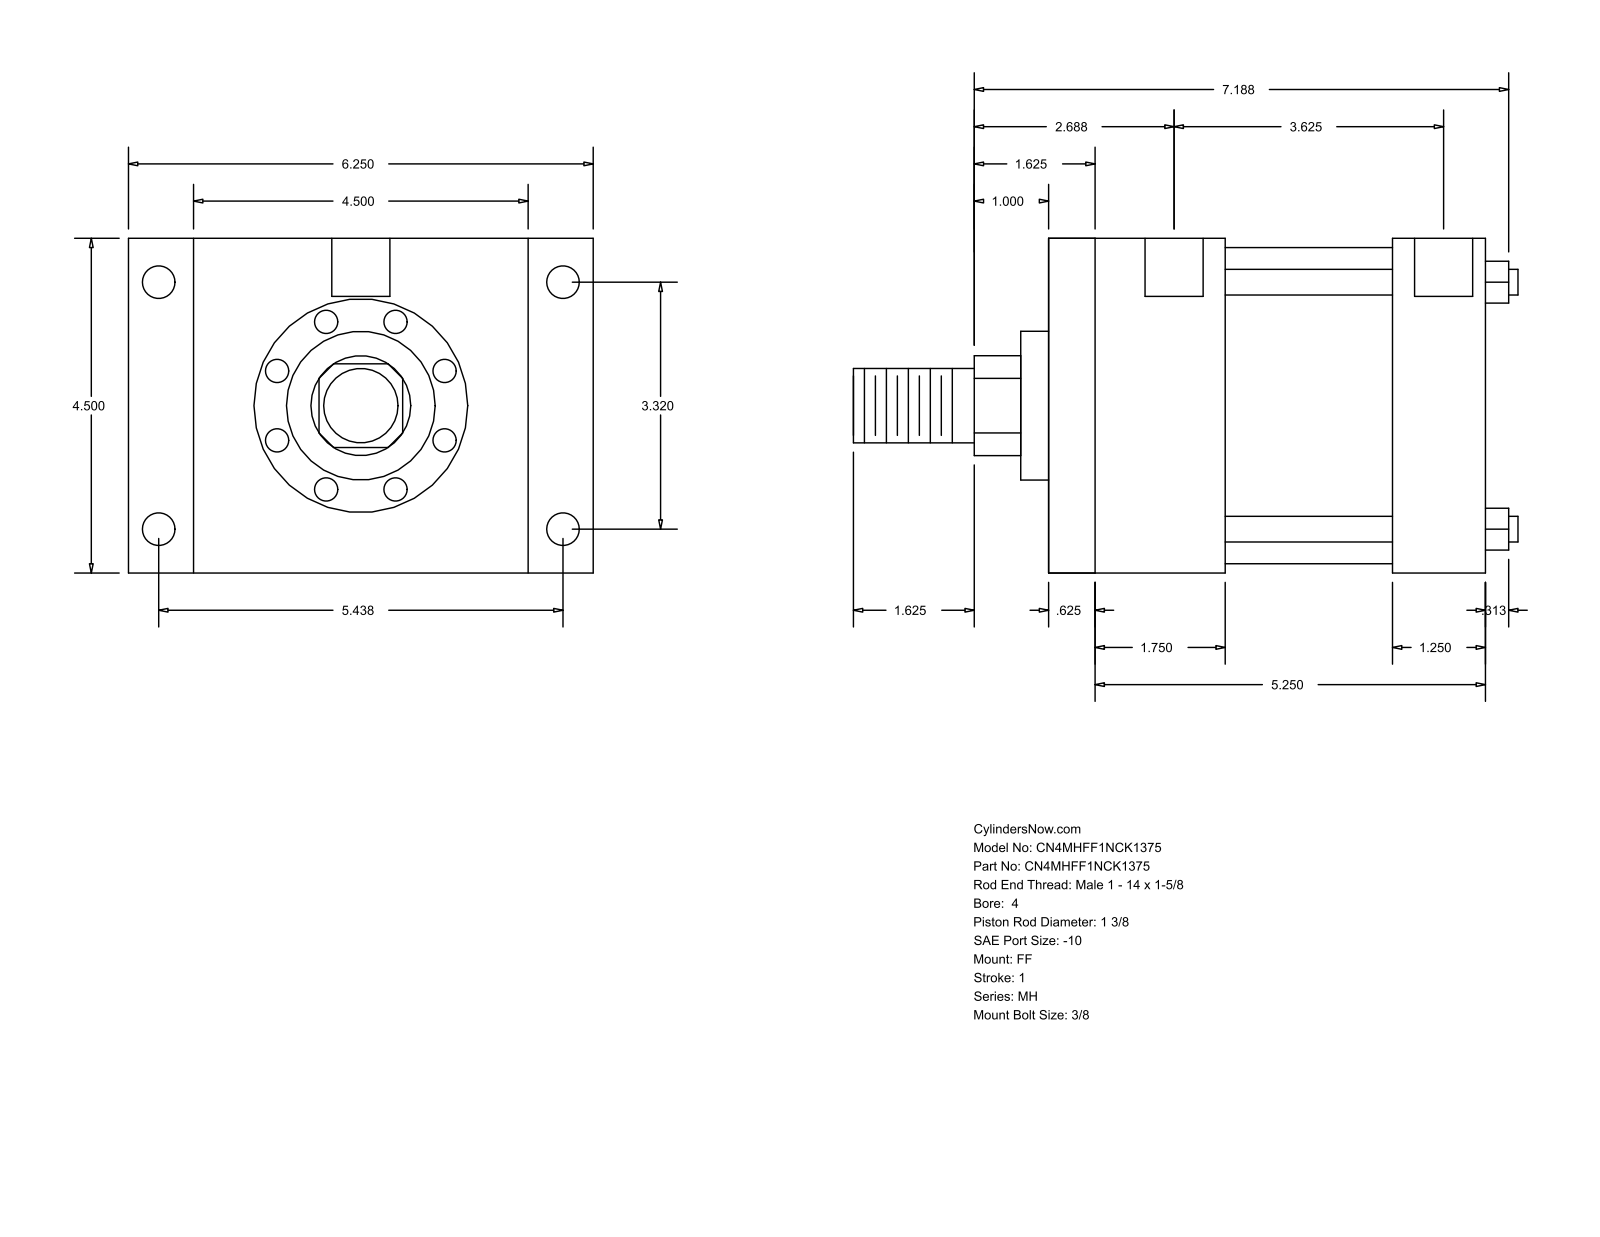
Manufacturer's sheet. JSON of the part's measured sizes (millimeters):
{"part_name": "MH_FF__0400_1.375", "step_written_by": "GSSL Pune (CONFIG_CONTROL_DESIGN)", "units": "millimeters", "bodies": {"solids": 0, "faces": 92, "planar": 64, "cylindrical": 28, "other": 0}, "overall_size": [227.01, 158.75, 114.3], "round_holes": [[8.73, 4], [11.13, 4], [19.84, 2]], "round_bosses_or_shafts": [[8.76, 4], [107.95, 1], [50.8, 1], [34.92, 1], [25.4, 1]], "partial_cylinders_radius": [[17.06, 1]], "face_to_face_distances": [114.3, 149.22, 15.87, 133.35, 60.32, 44.45, 88.9, 117.48, 101.61, 57.16], "hole_center_spacings": [1.59, 84.32, 93.67, 95.26, 138.12, 161.82, 92.08]}
